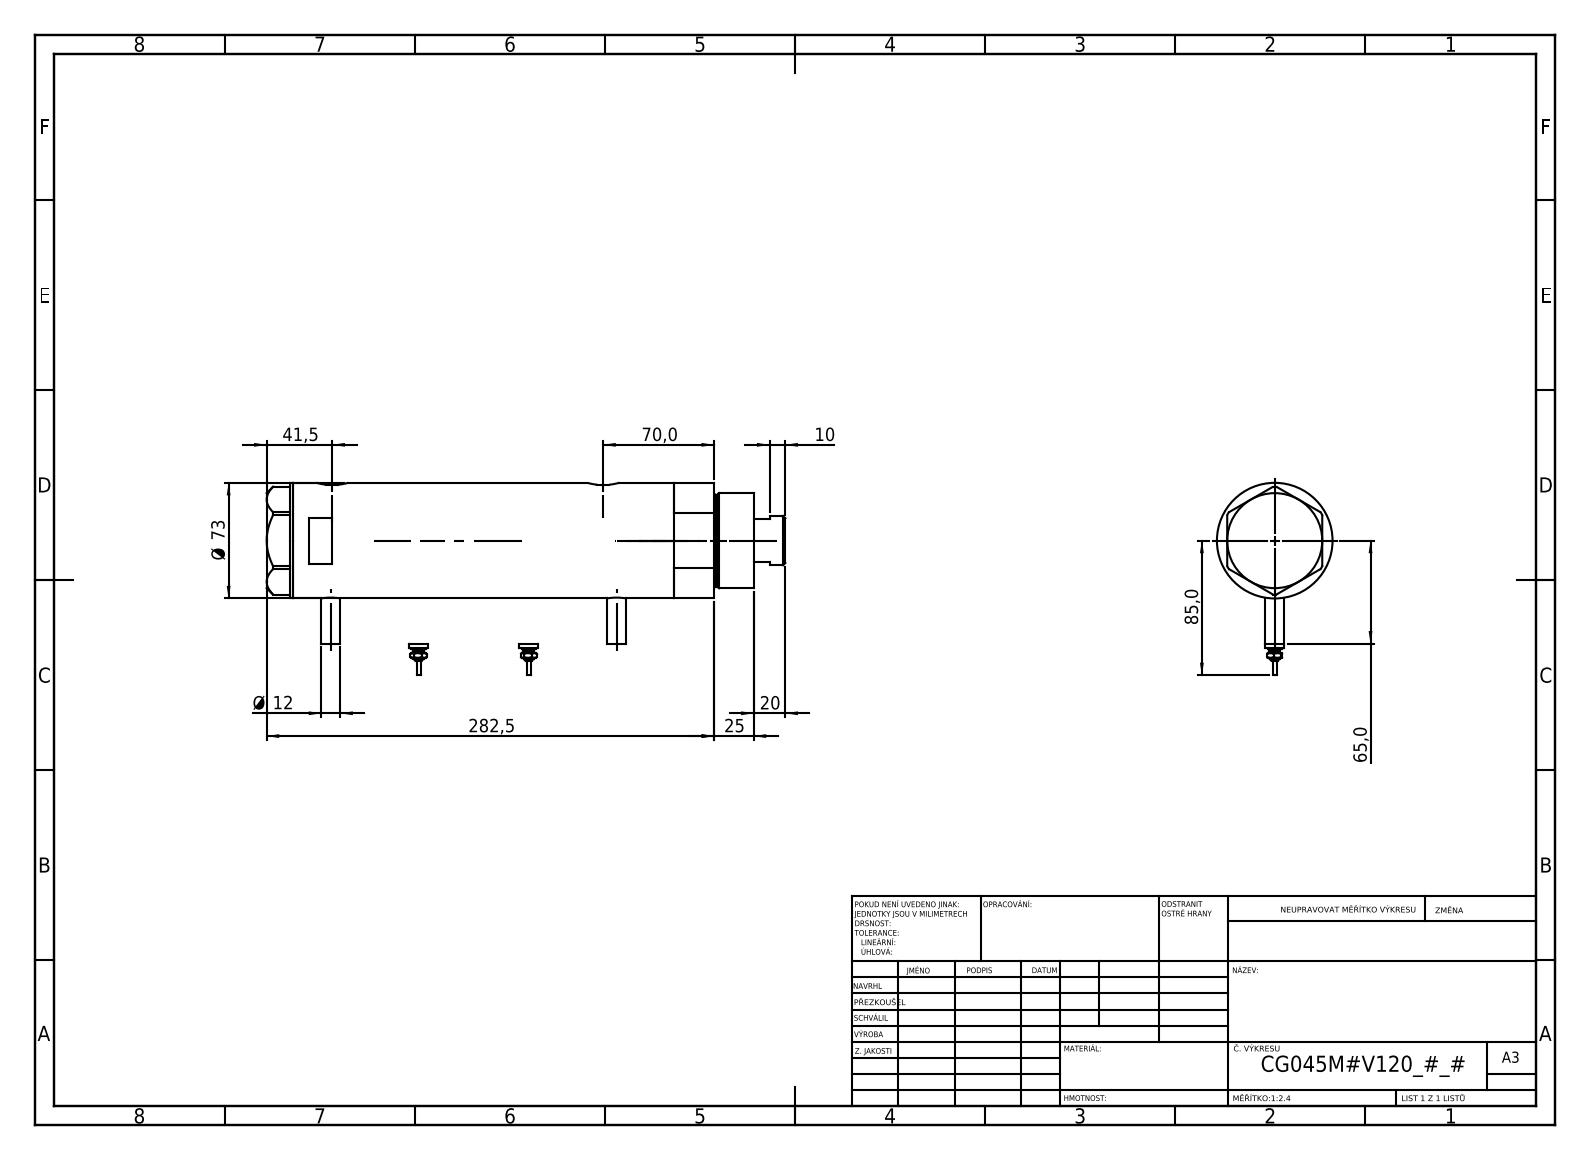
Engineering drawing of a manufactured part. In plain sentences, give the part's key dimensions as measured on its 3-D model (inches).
The part is named "V270CG_MIDDLE; V270CG_FRONT; Switch; V270CG_VC (+1 more)". Its 3-D file was written by "SolidWorks 2019 (CONFIG_CONTROL_DESIGN)". It is 6 solids with 212 faces: 77 planar, 71 cylindrical and 64 other. Overall it measures 12.894 by 4.783 by 2.874 inches. Its volume is 70.24 cubic inches and its surface area 290.3 square inches. Round holes: 2 of diameter 0.492, 2 of diameter 0.518, 1 of diameter 0.413, 1 of diameter 1.26, 1 of diameter 1.319, 1 of diameter 1.772, 1 of diameter 1.89, 1 of diameter 2.52. Round bosses or shafts: 4 of diameter 0.472, 2 of diameter 0.354, 2 of diameter 0.276, 2 of diameter 0.177, 2 of diameter 0.098, 1 of diameter 2.874, 1 of diameter 2.362, 1 of diameter 2.283. Partial cylindrical surfaces (rounded edges, fillets, slot ends): 2 of radius 0.394. The main face-to-face distances are 7.717, 1.024, 6.693, 0.65, 1.673, 8.366, 0.079, 11.457, 12.106, 10.433. The hole center spacings are 0.039, 0.335, 6.732, 6.772, 7.067, 7.106.
